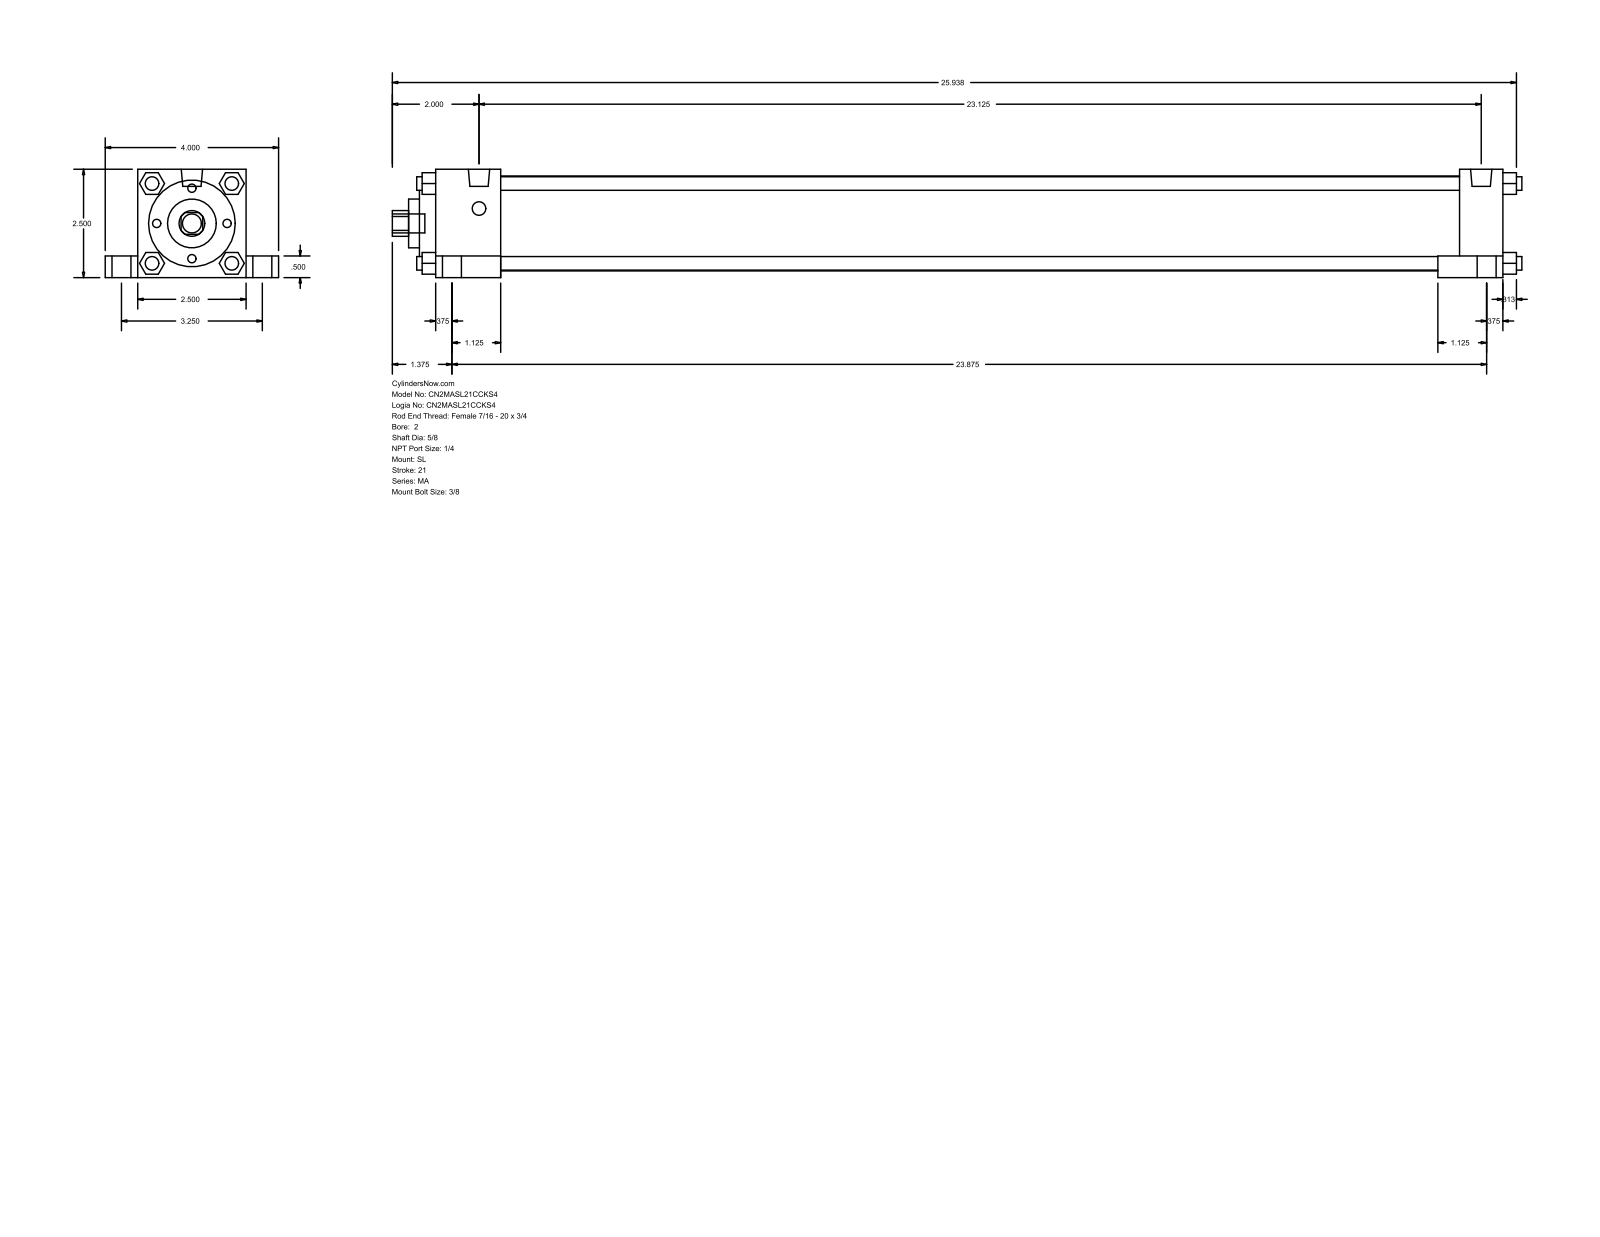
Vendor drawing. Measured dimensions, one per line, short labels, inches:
name: MA_SL__0200_0.625
written by: GSSL Pune (CONFIG_CONTROL_DESIGN)
unit: in
bodies: 0 solids, 150 faces (113 planar, 37 cylindrical, 0 other)
size: 26.063 × 4 × 2.5
holes: 1× ⌀0.625, 1× ⌀1.125, 1× ⌀2, 1× ⌀2.19
bosses: 8× ⌀0.313, 5× ⌀0.437, 4× ⌀0.687, 2× ⌀0.492
rounds: 1× R0.297
face distances: 2.5, 0.5, 0.375, 1, 0.75, 3.25, 1.5, 24.625, 2, 23.125
